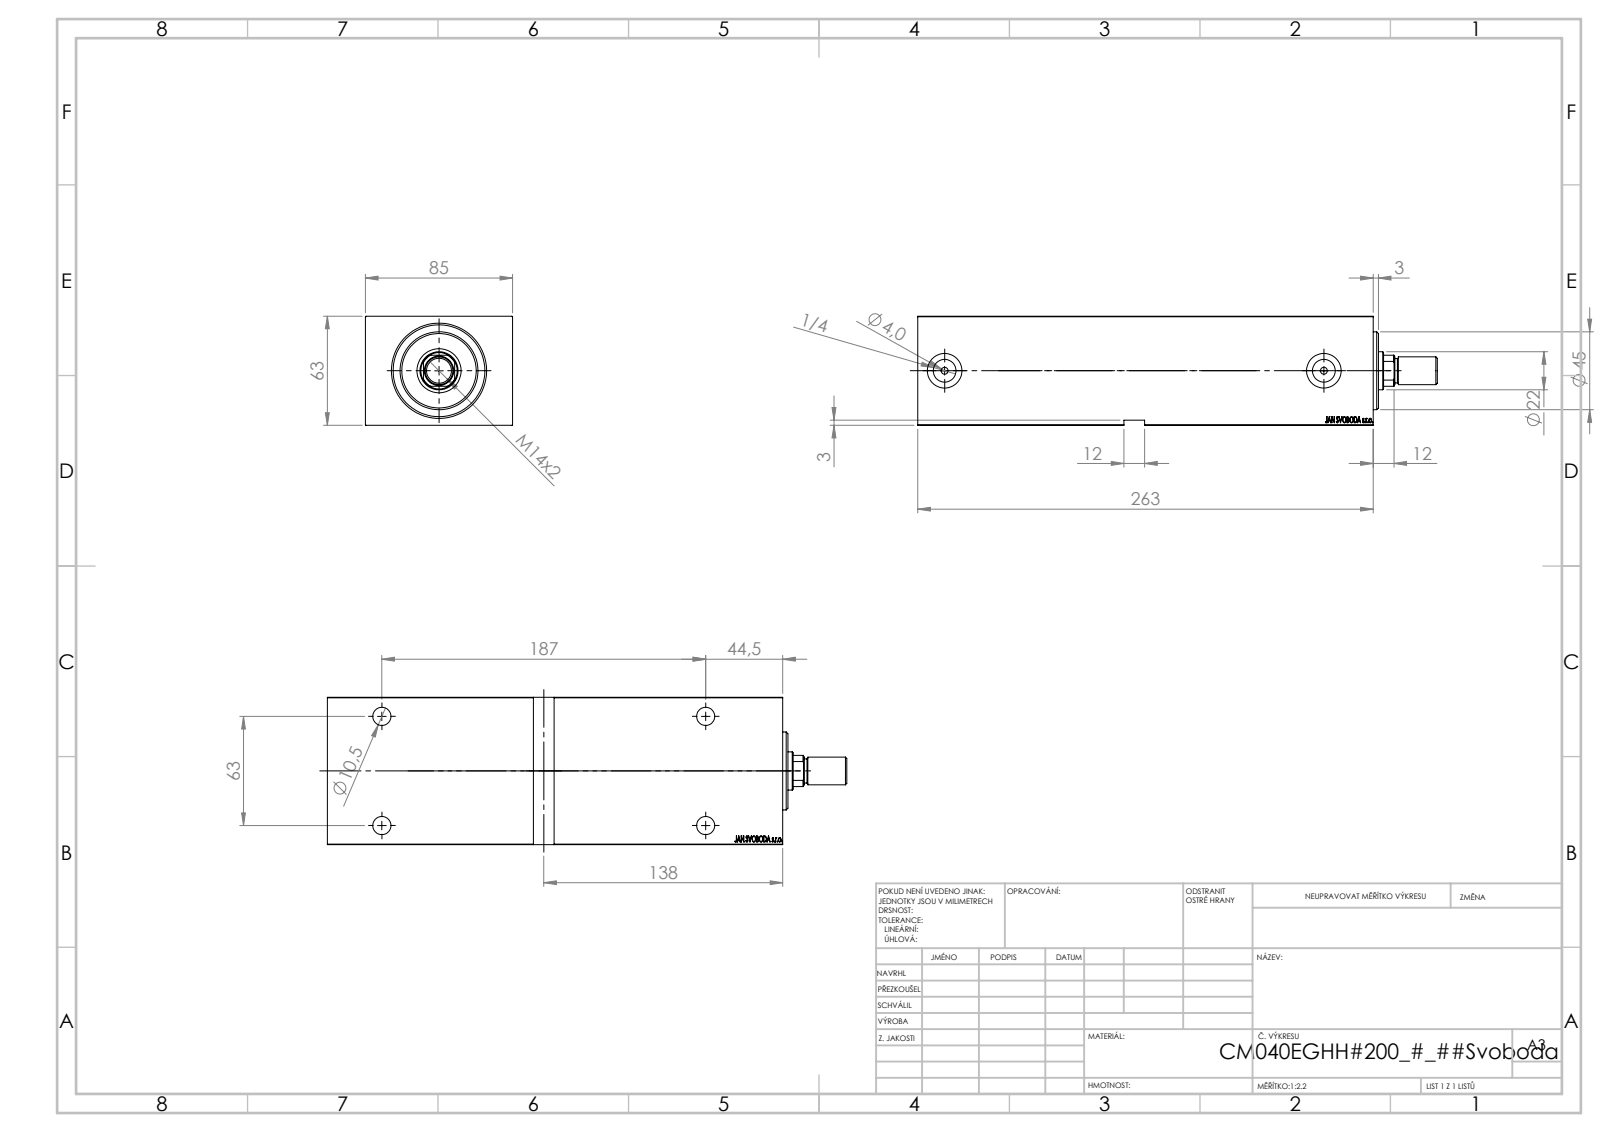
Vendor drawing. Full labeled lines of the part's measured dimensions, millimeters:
Part name (STEP PRODUCT): V450CM_E_VCP; V450CM_MALE_METRIC; V450CM_E_Body; V450CM_VC_B
STEP written by: SolidWorks 2019 (CONFIG_CONTROL_DESIGN)
Units: millimetres
Bodies: 4 solids, 870 faces (414 planar, 56 cylindrical, 400 other)
Overall size (bounding box): 300 × 85 × 63
Volume: 1 211 000 mm³ · Surface area: 163 864 mm²
Round holes (diameter × count): ⌀10.5 ×4, ⌀16.5 ×4, ⌀4 ×2, ⌀13.16 ×2, ⌀20 ×2, ⌀12.5 ×1, ⌀22 ×1, ⌀25.5 ×1, ⌀40 ×1, ⌀53 ×1
Round bosses / shafts (diameter × count): ⌀45 ×1, ⌀42 ×1, ⌀16 ×1, ⌀14 ×1
Partial cylindrical surfaces — rounded edges, fillets, slot ends (radius × count): R10.5 ×1
Main face-to-face distances: 63, 85, 263, 12, 251, 3, 5, 258, 246, 60
Hole centre spacings: 63, 187, 197.33, 219
